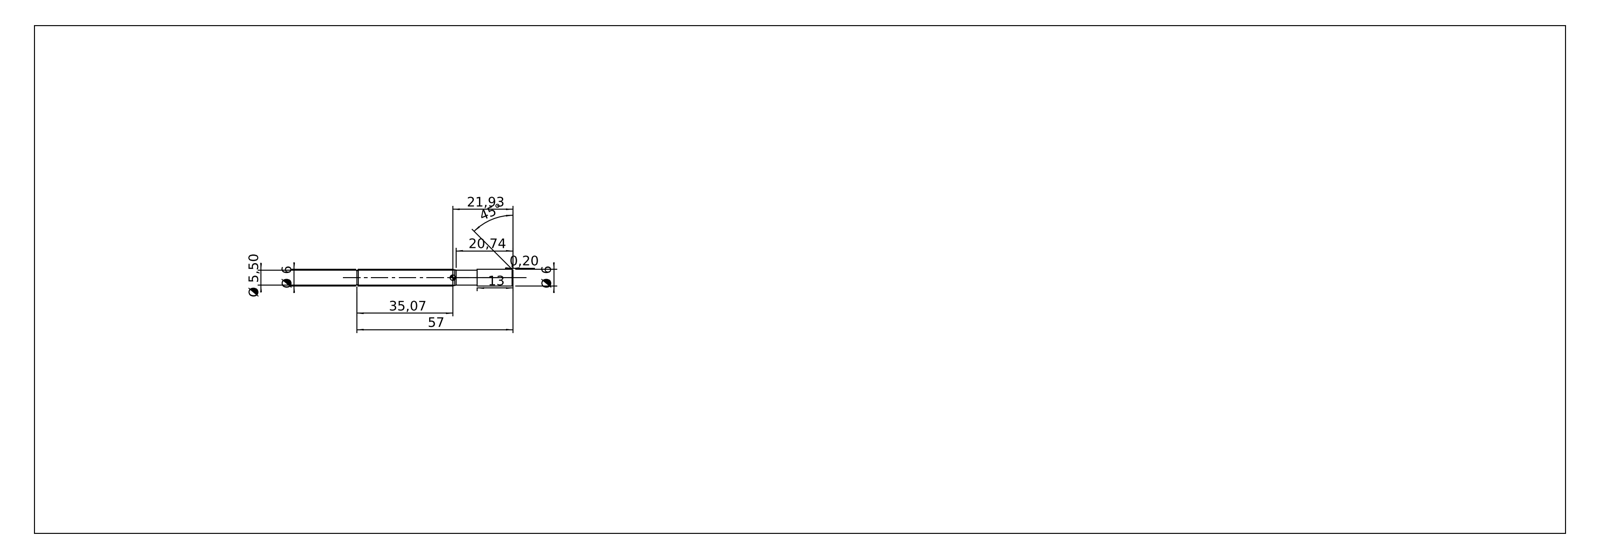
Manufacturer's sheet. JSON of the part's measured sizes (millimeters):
{"part_name": "738.060.00", "step_written_by": "SolidWorks 2019 (CONFIG_CONTROL_DESIGN)", "units": "millimeters", "bodies": {"solids": 2, "faces": 11, "planar": 4, "cylindrical": 3, "other": 4}, "overall_size": [57, 6, 6], "volume_mm3": 1570, "surface_area_mm2": 1161, "round_bosses_or_shafts": [[6, 1], [5.5, 1]], "face_to_face_distances": [13, 57, 44]}
